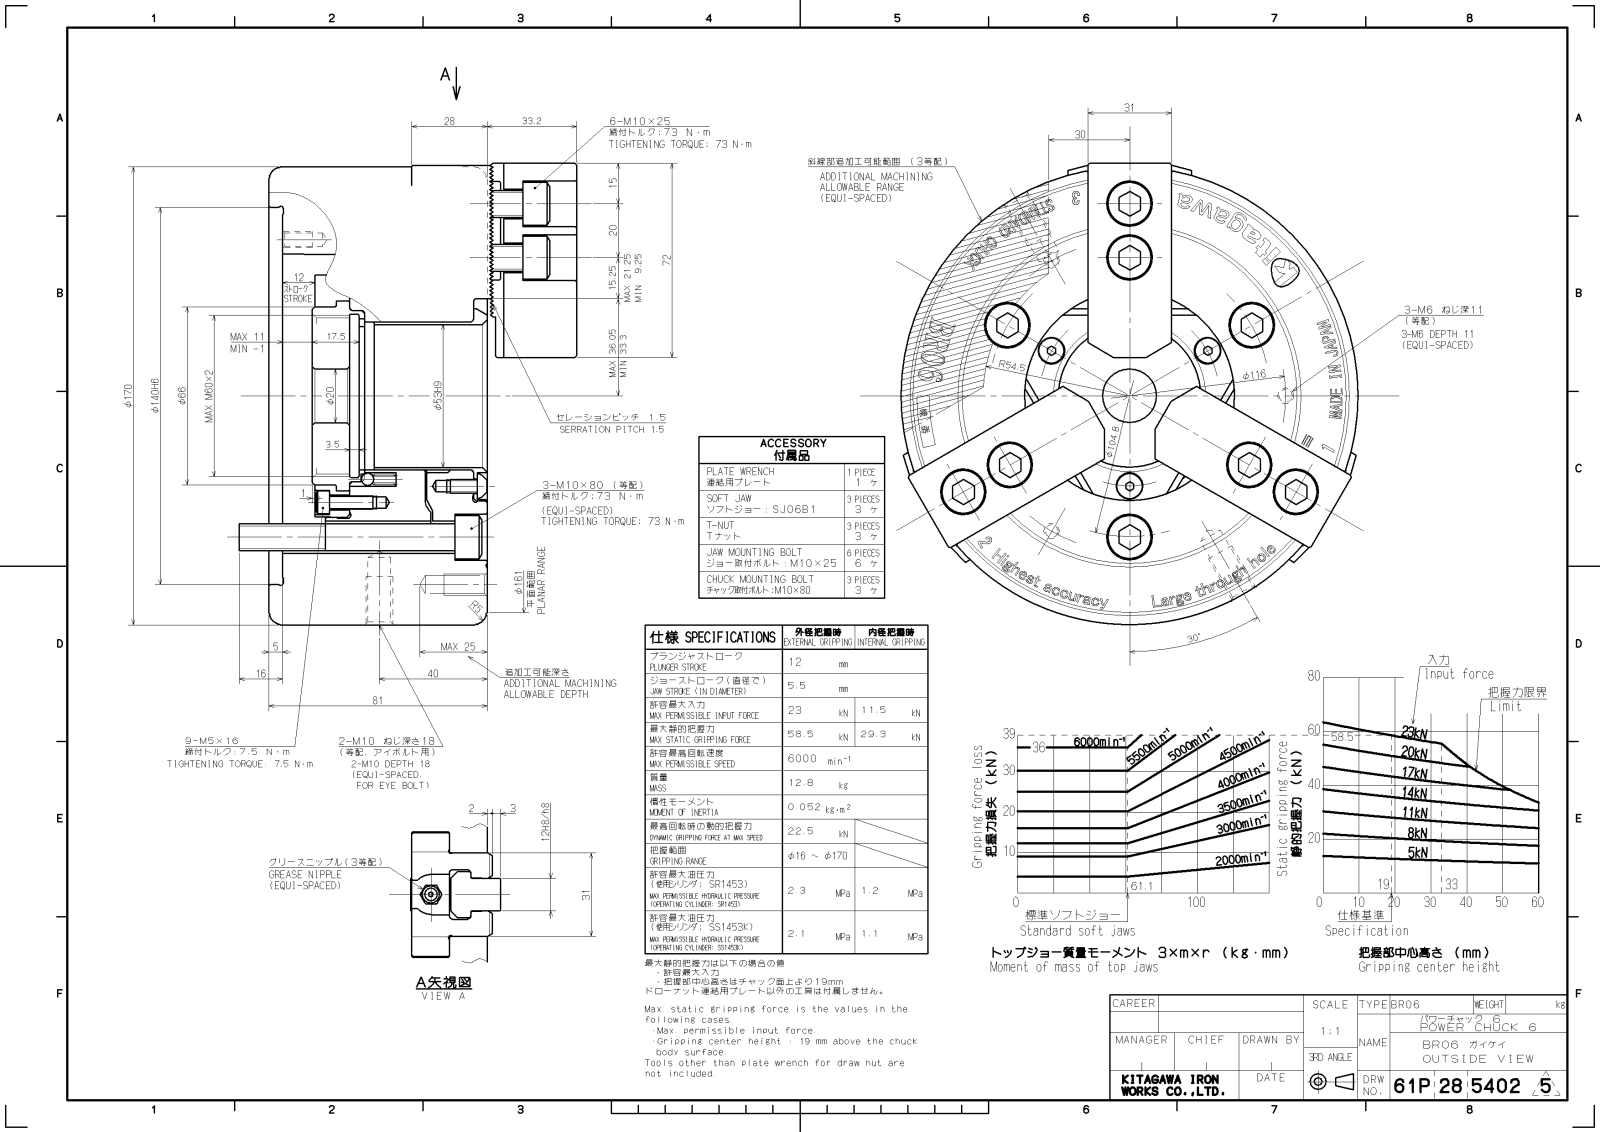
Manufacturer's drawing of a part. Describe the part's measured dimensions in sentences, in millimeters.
The part is named "BR06-Solid". Its 3-D file was written by "ST-DEVELOPER v16.7 (AUTOMOTIVE_DESIGN)". It is 1 solid with 2394 faces: 2016 planar, 220 cylindrical and 158 other. Overall it measures 171.3 by 170 by 125.2 millimeters. Its volume is 1 673 000 cubic millimeters and its surface area 212 764 square millimeters. Round holes: 15 of diameter 5, 12 of diameter 4.2, 12 of diameter 5.5, 10 of diameter 9, 10 of diameter 10, 9 of diameter 17, 6 of diameter 6, 6 of diameter 11, 3 of diameter 1.5, 3 of diameter 1.9, 3 of diameter 5.3, 3 of diameter 12. Round bosses or shafts: 9 of diameter 16, 9 of diameter 8.5, 3 of diameter 10, 3 of diameter 9.5, 1 of diameter 170, 1 of diameter 90. Partial cylindrical surfaces (rounded edges, fillets, slot ends): 18 of radius 1.2, 8 of radius 8, 6 of radius 1, 6 of radius 6, 3 of radius 7.5, 3 of radius 28, 1 of radius 39. The main face-to-face distances are 5, 76, 14, 31, 16, 81, 51, 17, 109.2, 33.2. The hole center spacings are 39.5, 68.42, 13.72, 13.99, 20.39, 46.54, 48.26, 59.06.
